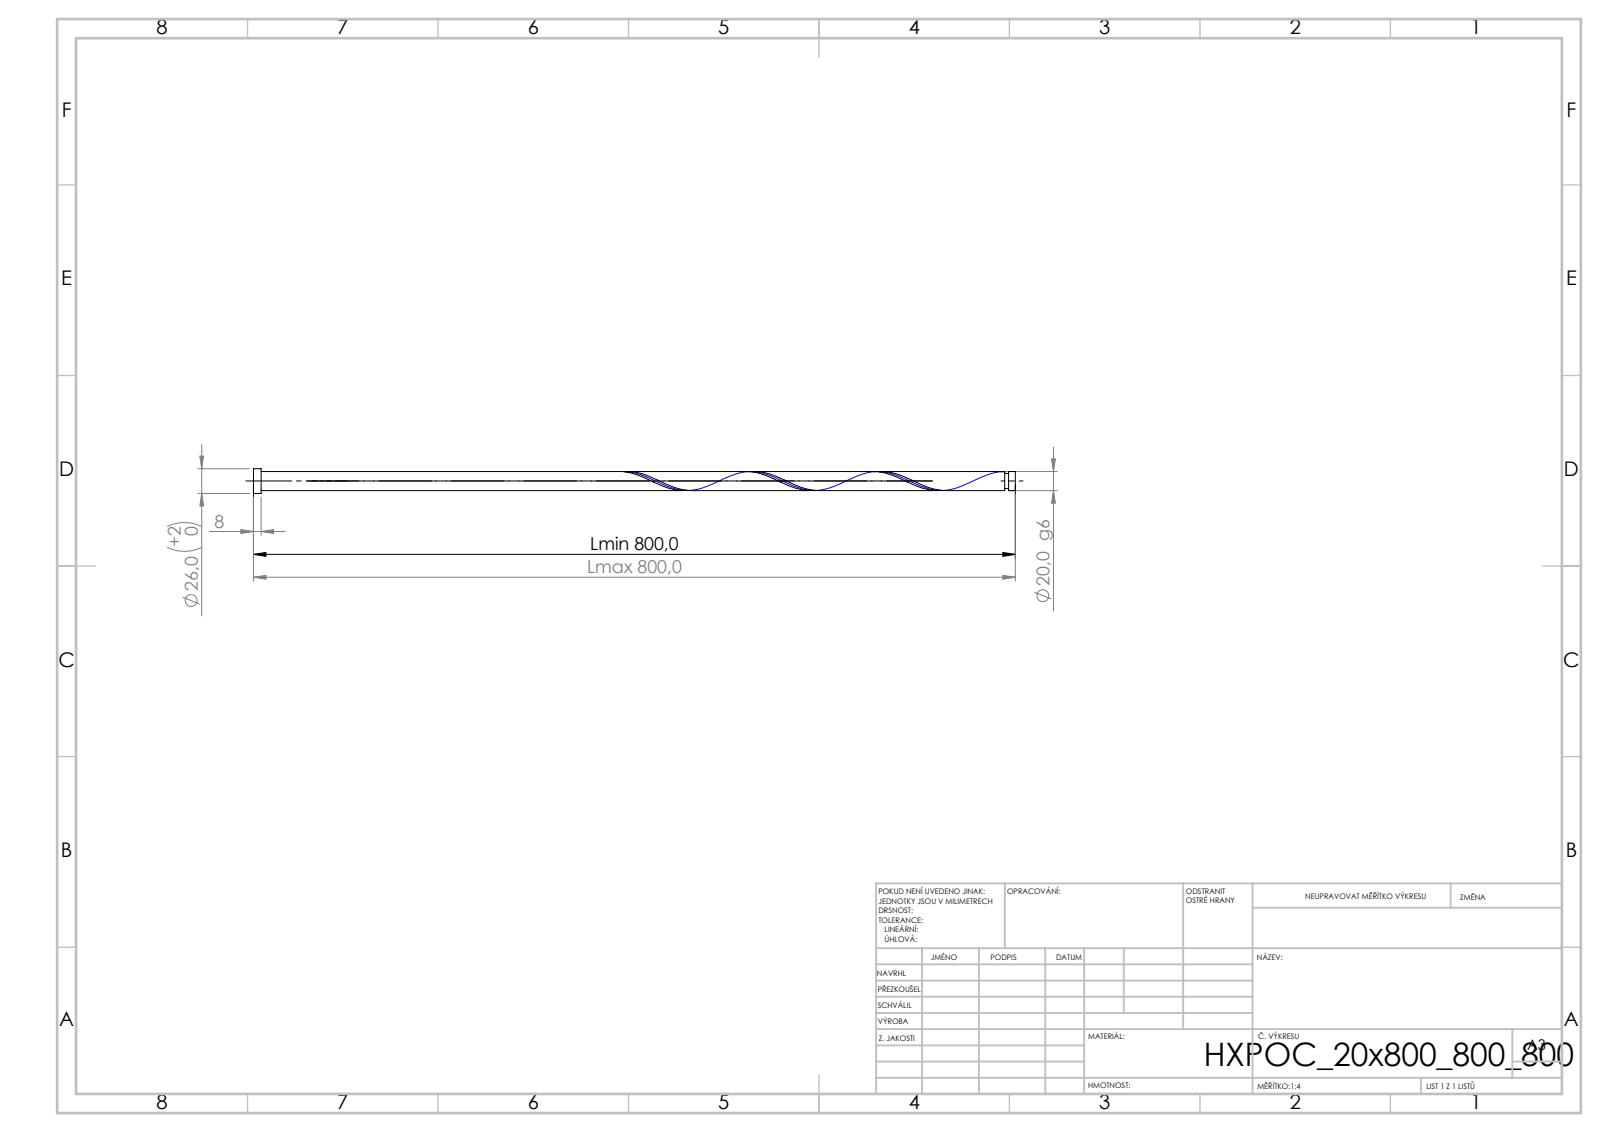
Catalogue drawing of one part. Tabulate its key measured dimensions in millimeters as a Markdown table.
| quantity | value |
| --- | --- |
| STEP written by | SolidWorks 2019 (CONFIG_CONTROL_DESIGN) |
| units | millimeters |
| bodies | 1 solid, 21 faces (6 planar, 14 cylindrical, 1 other) |
| overall size | 800 × 26 × 26 |
| volume | 250 203 mm³ |
| surface area | 52 522 mm² |
| round bosses / shafts (diameter × count) | 26 × 1, 20 × 1, 16 × 1 |
| main face-to-face distances | 800, 8, 792, 792.9, 784.9, 7.1, 788.9, 780.9, 4, 11.1 |
